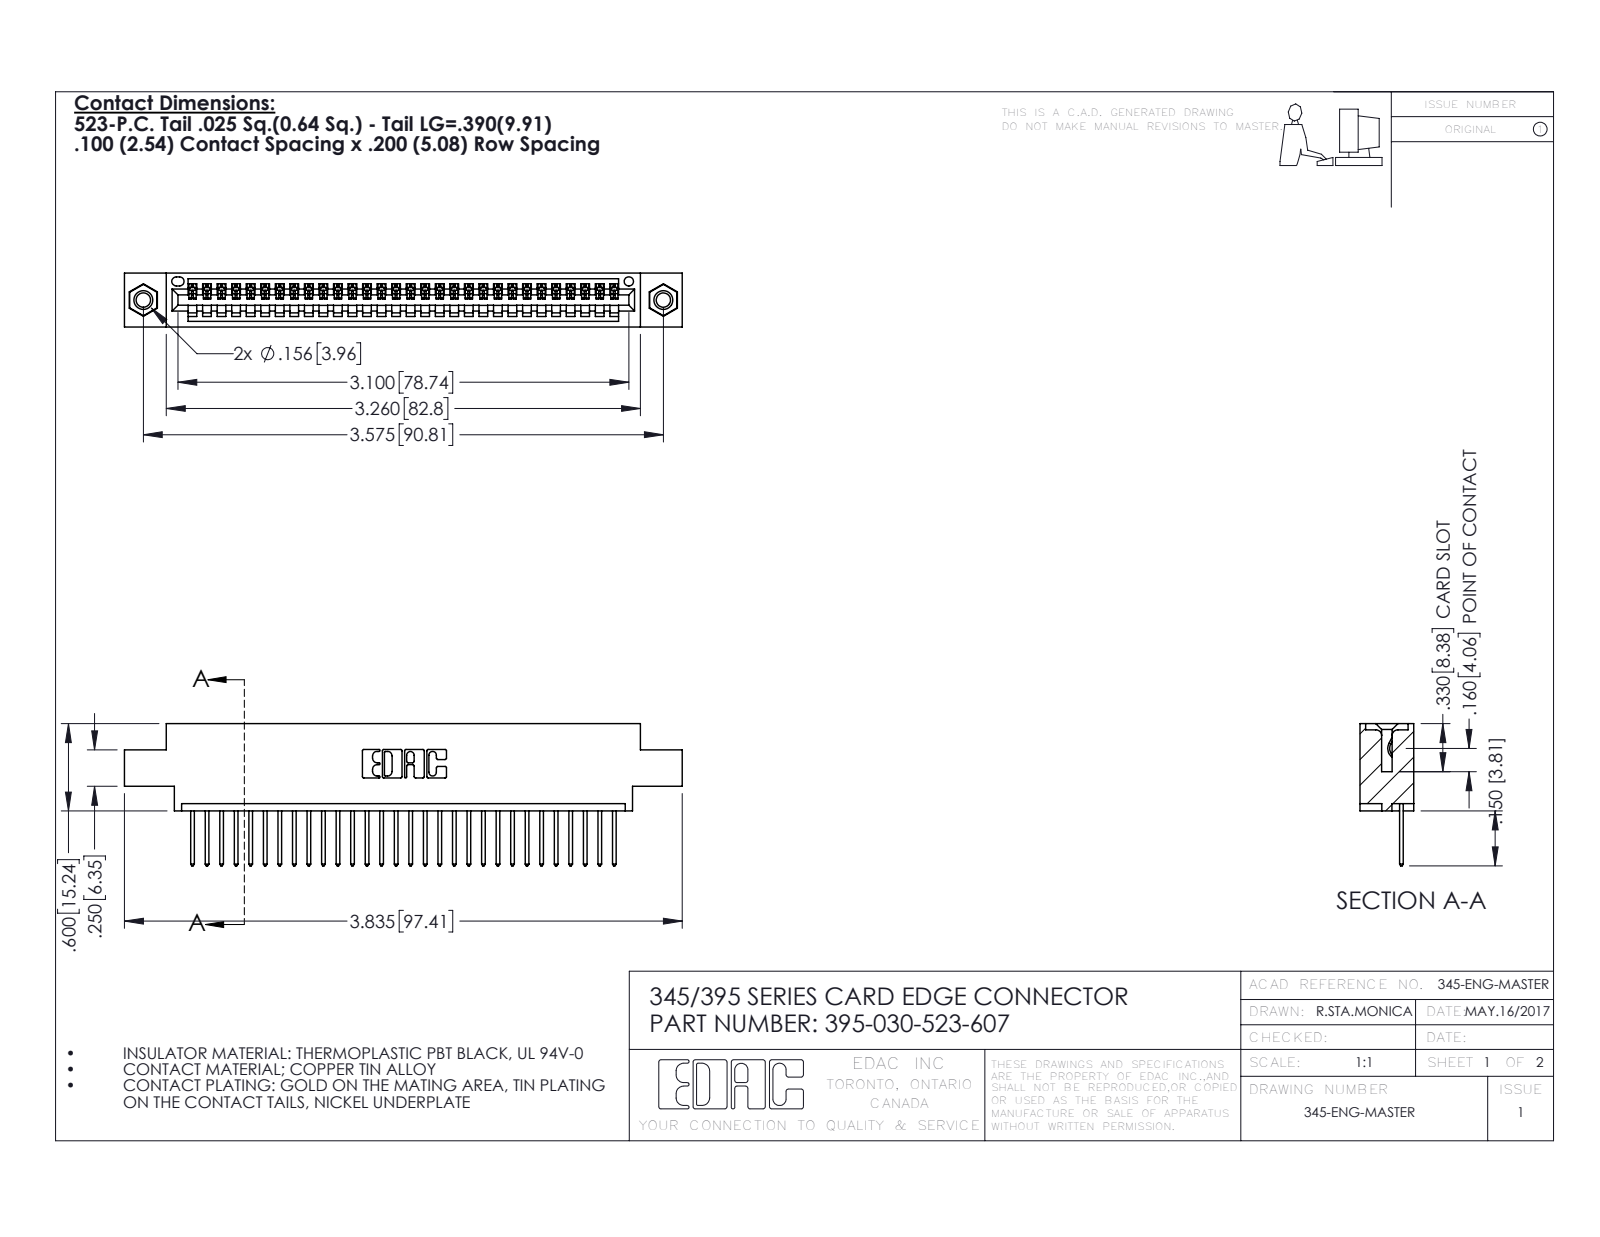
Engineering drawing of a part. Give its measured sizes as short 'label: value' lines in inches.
name: 345-292-001_345-293-123; 345 Part_0.170 Offset - 0.156 Dia-TI; 395-030-523-607; 345-250-001_345-250-005-103
written by: SolidWorks 2016 (CONFIG_CONTROL_DESIGN)
unit: in
bodies: 33 solids, 1930 faces (1316 planar, 598 cylindrical, 16 other)
size: 3.835 × 0.977 × 0.37
volume: 0.55 in³; area: 18.61 in²
holes: 2× ⌀0.098, 2× ⌀0.125, 2× ⌀0.156, 1× ⌀0.064
bosses: 2× ⌀0.155
rounds: 60× R0.006, 60× R0.01, 22× R0.01, 6× R0.007, 6× R0.031, 3× R0.026, 2× R0.031, 2× R0.04
face distances: 0.072, 0.298, 0.37, 0.2, 0.098, 0.272, 0.025, 0.225, 0.175, 0.149
hole spacings: 0.27, 3.34, 3.575
